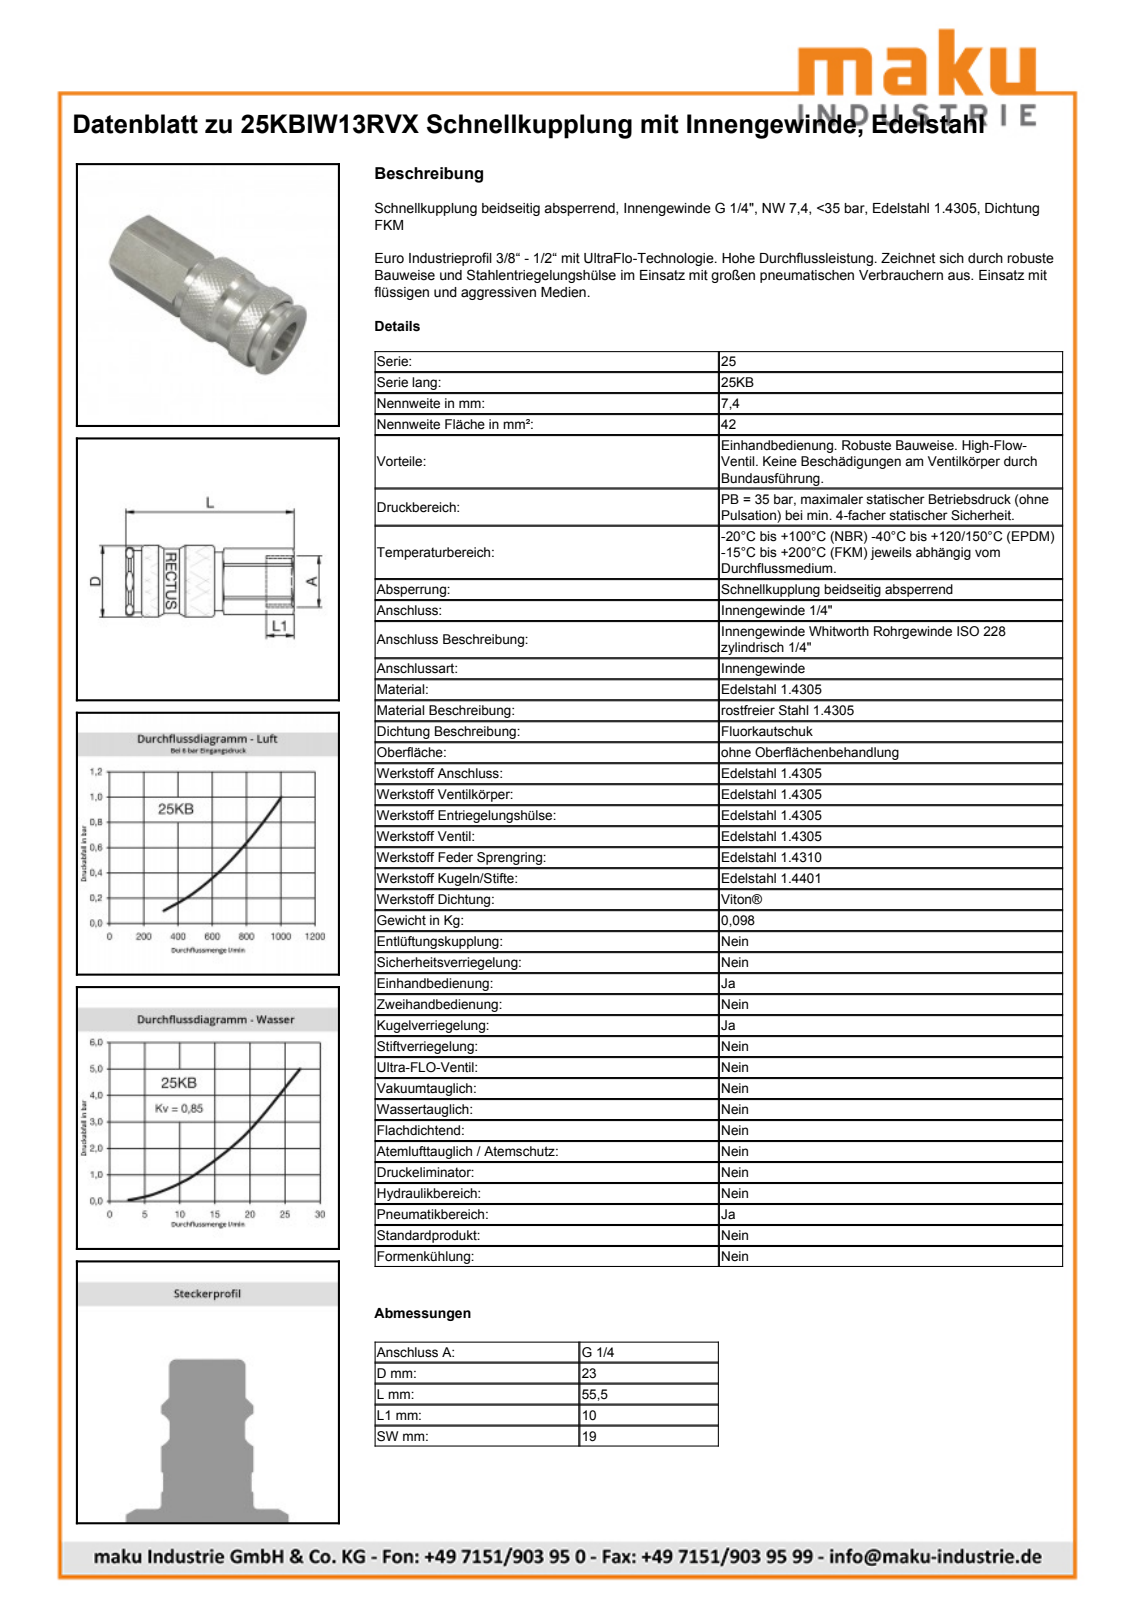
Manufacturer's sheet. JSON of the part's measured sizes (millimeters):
{"part_name": "D109498", "step_written_by": "Autodesk Inventor 2013 (AUTOMOTIVE_DESIGN)", "units": "millimeters", "bodies": {"solids": 2, "faces": 602, "planar": 211, "cylindrical": 83, "other": 308}, "overall_size": [55.5, 23.15, 23.15], "volume_mm3": 17410, "surface_area_mm2": 8224, "round_holes": [[11.45, 1], [14, 1], [15.6, 1], [17.25, 1], [19.35, 1], [20.05, 1]], "round_bosses_or_shafts": [[23.15, 1], [21, 1], [20, 1], [18.95, 1], [16, 1], [15.3, 1], [15.11, 1]], "partial_cylinders_radius": [[10.4, 1], [10.7, 1], [11, 1]], "face_to_face_distances": [19.6, 45.49, 55.5, 10.01, 21, 24.5, 20.99, 31, 5.25, 19.25]}
